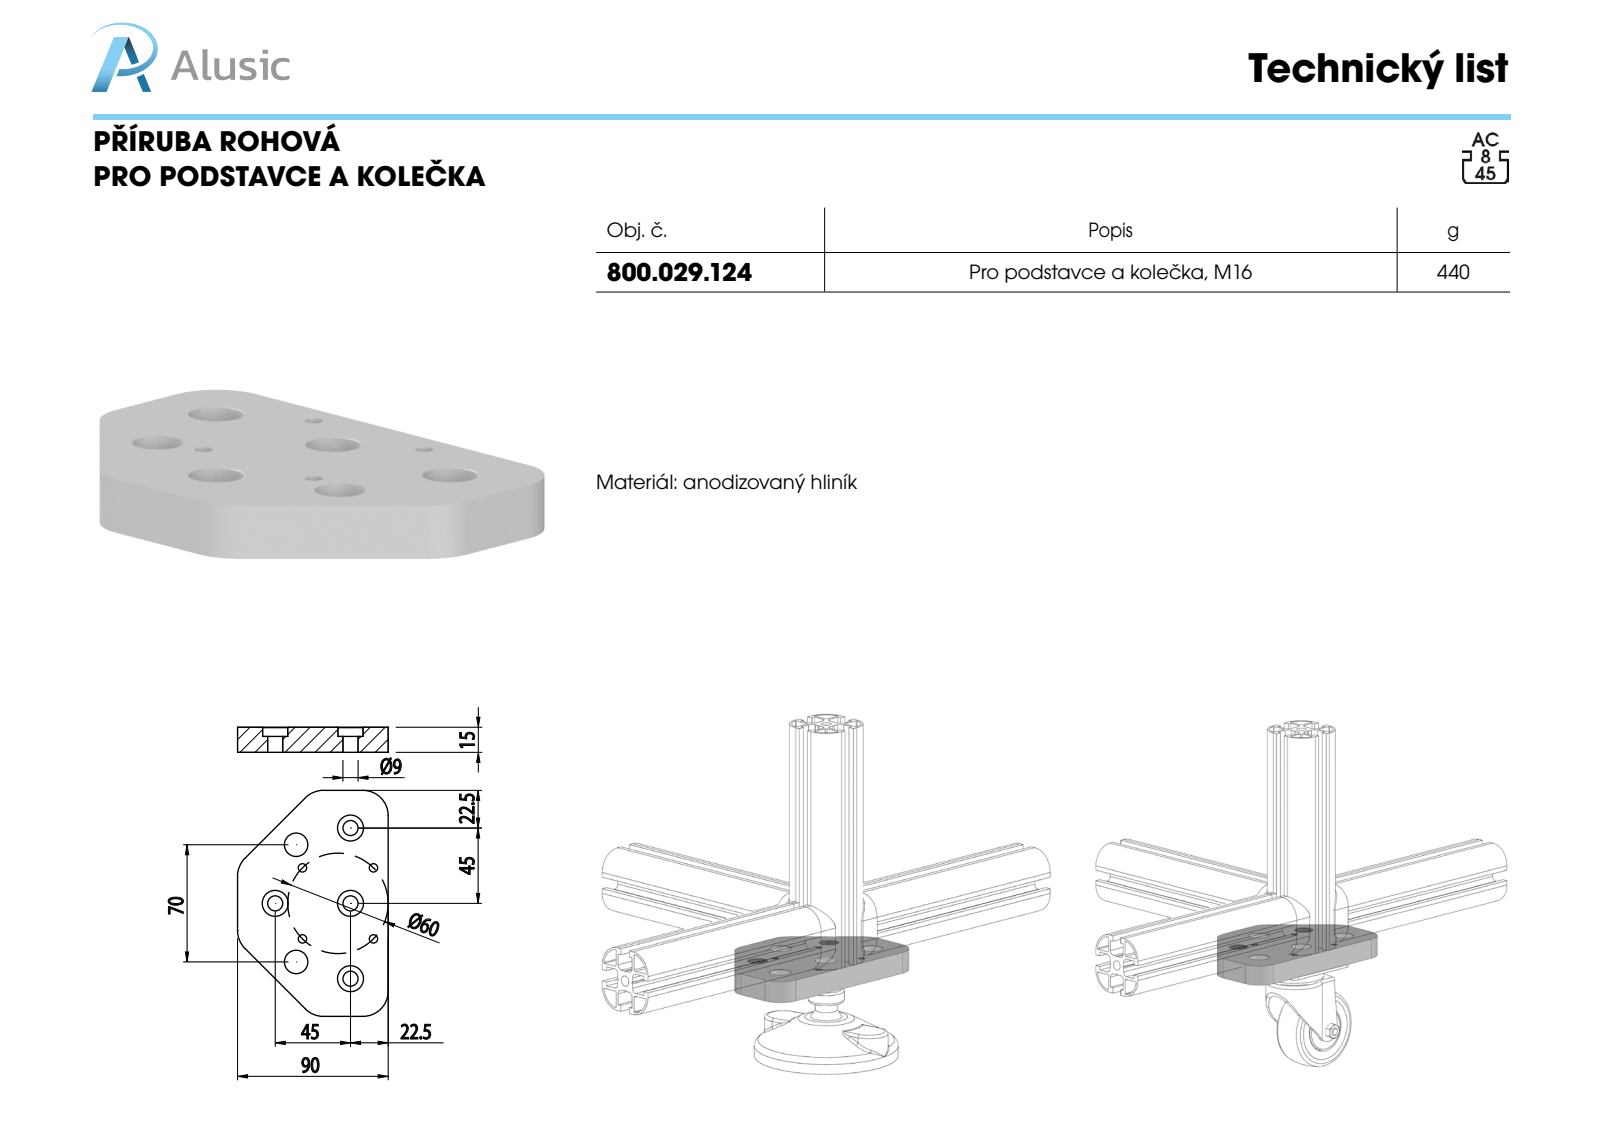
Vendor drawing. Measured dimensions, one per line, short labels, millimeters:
name: 800.029.124
written by: SolidWorks 2011 (CONFIG_CONTROL_DESIGN)
unit: mm
bodies: 1 solid, 54 faces (12 planar, 34 cylindrical, 8 other)
size: 135 × 90 × 15
volume: 138 029 mm³; area: 28 810 mm²
holes: 4× ⌀5, 4× ⌀9, 4× ⌀15, 2× ⌀14
rounds: 6× R15
face distances: 15, 90, 9.5, 5.5, 135
hole spacings: 42.42, 45, 14.3, 25.26, 26.74, 27.46, 34, 35.69
